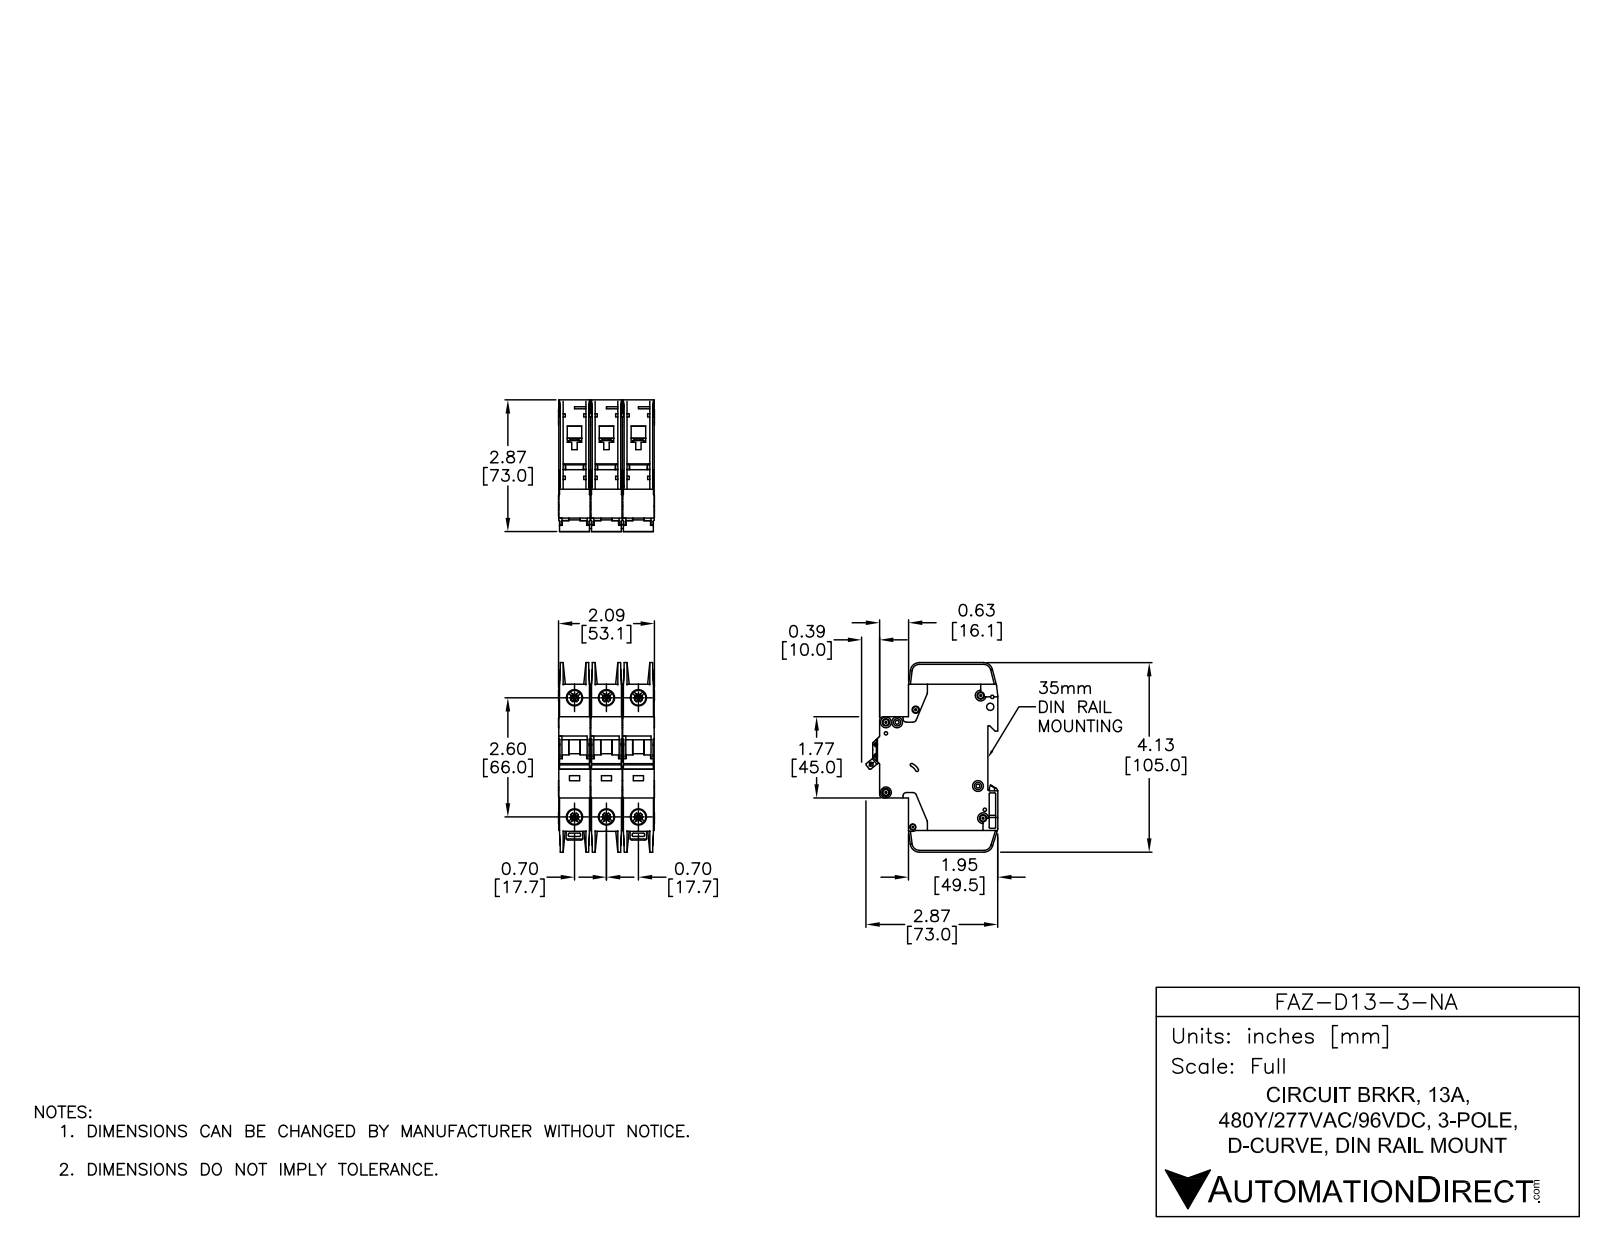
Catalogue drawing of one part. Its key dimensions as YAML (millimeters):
part_name: "FAZ-D13-3-NA"
step_written_by: "SolidWorks 2014 (AUTOMOTIVE_DESIGN)"
units: millimeters
bodies: {solids: 9, faces: 2352, planar: 1227, cylindrical: 789, other: 336}
overall_size: [105, 73.04, 53.1]
volume: 233085
surface_area: 74219
round_holes:
  - {diameter: 3.6, count: 7}
  - {diameter: 7.15, count: 6}
  - {diameter: 8.2, count: 6}
  - {diameter: 1.09, count: 2}
  - {diameter: 1.5, count: 2}
  - {diameter: 4, count: 2}
  - {diameter: 1.9, count: 1}
  - {diameter: 2.15, count: 1}
  - {diameter: 2.2, count: 1}
  - {diameter: 2.55, count: 1}
  - {diameter: 3.3, count: 1}
  - {diameter: 3.4, count: 1}
round_bosses_or_shafts:
  - {diameter: 6, count: 7}
  - {diameter: 2.5, count: 3}
partial_cylinders:
  - {radius: 0.25, count: 65}
  - {radius: 0.5, count: 30}
  - {radius: 1, count: 26}
  - {radius: 2, count: 14}
  - {radius: 1.8, count: 5}
  - {radius: 5, count: 5}
  - {radius: 4, count: 4}
  - {radius: 0.2, count: 2}
face_to_face_distances: [17.7, 35.4, 17.5, 35.2, 0.7, 15.05, 2.45, 1.75, 15.75, 13.3]
hole_center_spacings: [17.7, 68.33, 66, 6.2, 35.4, 74.89, 5.19, 6.1]
